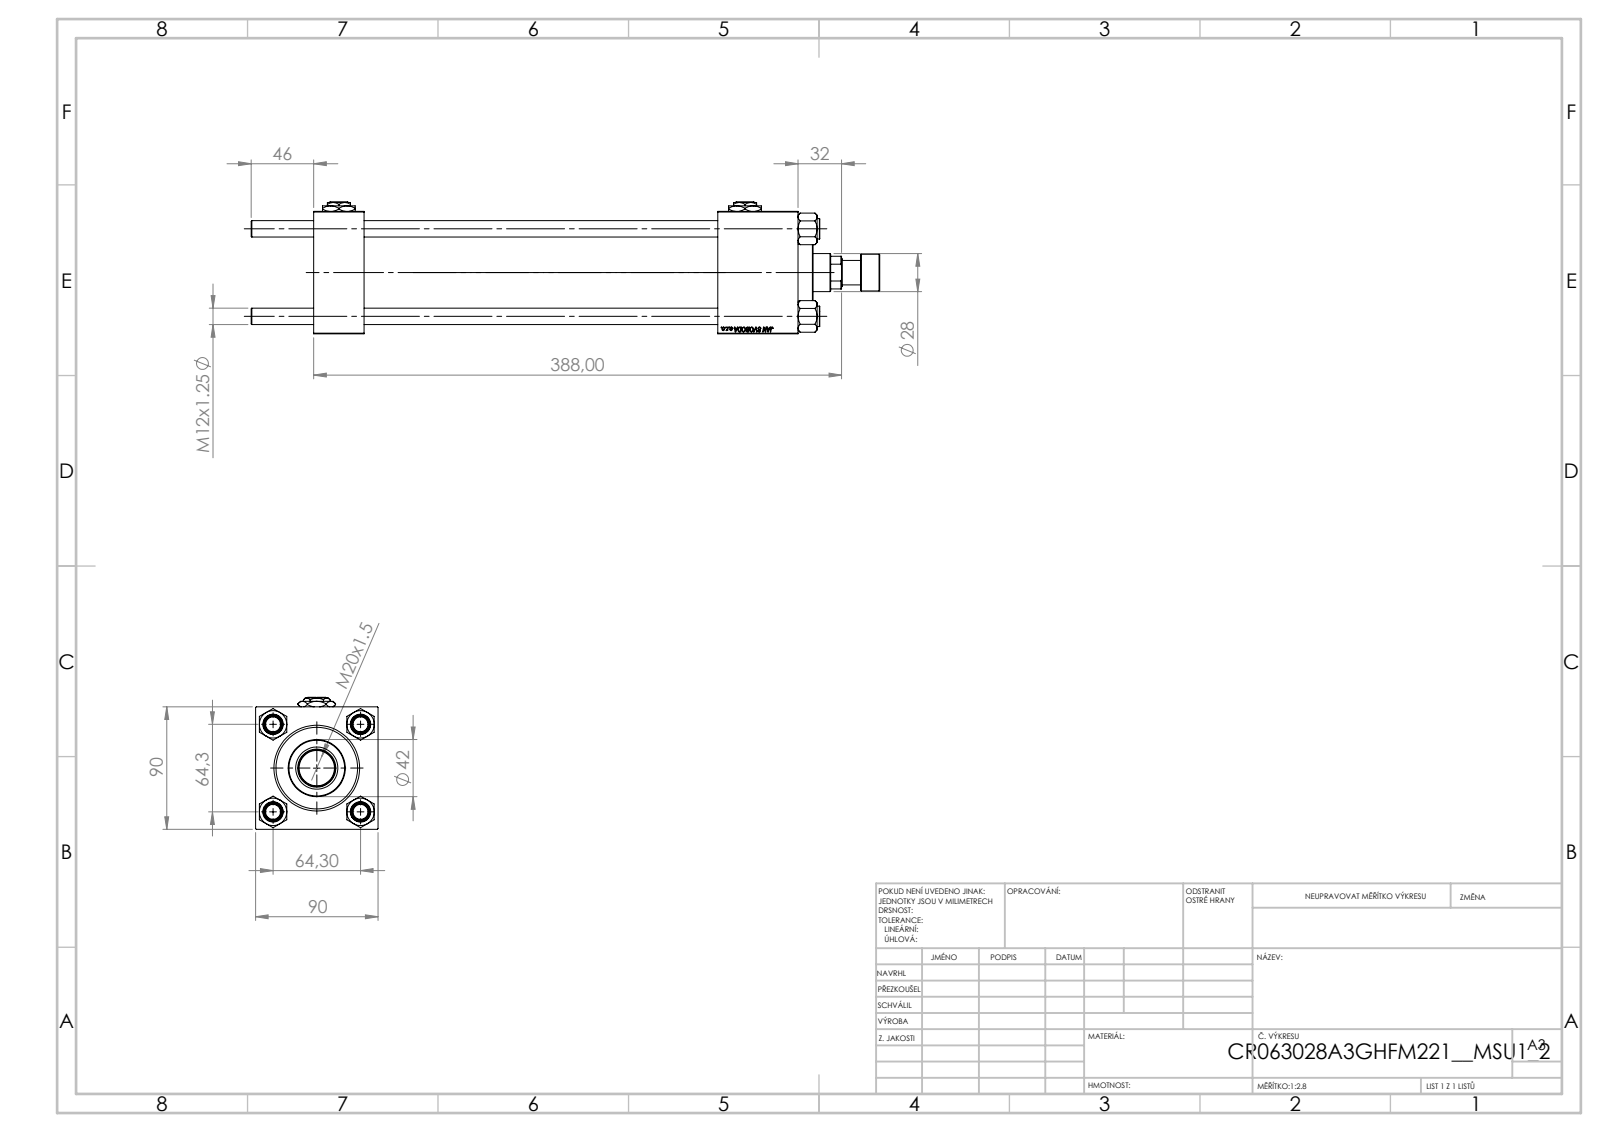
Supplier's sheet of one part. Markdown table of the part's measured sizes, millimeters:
| quantity | value |
| --- | --- |
| part name | CR025_012_A_0_G_A_G_M_020_+#_##_TYCINKA; V215_VC_A; Zatka_pro_OIL_PORT; V215CR_VCP (+3 more) |
| STEP written by | SolidWorks 2019 (CONFIG_CONTROL_DESIGN) |
| units | millimeters |
| bodies | 14 solids, 1247 faces (571 planar, 92 cylindrical, 584 other) |
| overall size | 462 × 97 × 90 |
| volume | 1 326 000 mm³ |
| surface area | 334 651 mm² |
| round holes (diameter × count) | 12 × 4, 7 × 2, 20.96 × 2, 30 × 2, 18.5 × 1, 28 × 1, 31 × 1, 50 × 1, 60 × 1, 63 × 1 |
| round bosses / shafts (diameter × count) | 15 × 4, 69 × 1, 42 × 1, 27 × 1, 18 × 1 |
| main face-to-face distances | 90, 37, 356, 319, 59, 297, 260, 327.3, 290.3, 30.3 |
| hole center spacings | 45.47, 64.3, 90.93, 298.5 |
